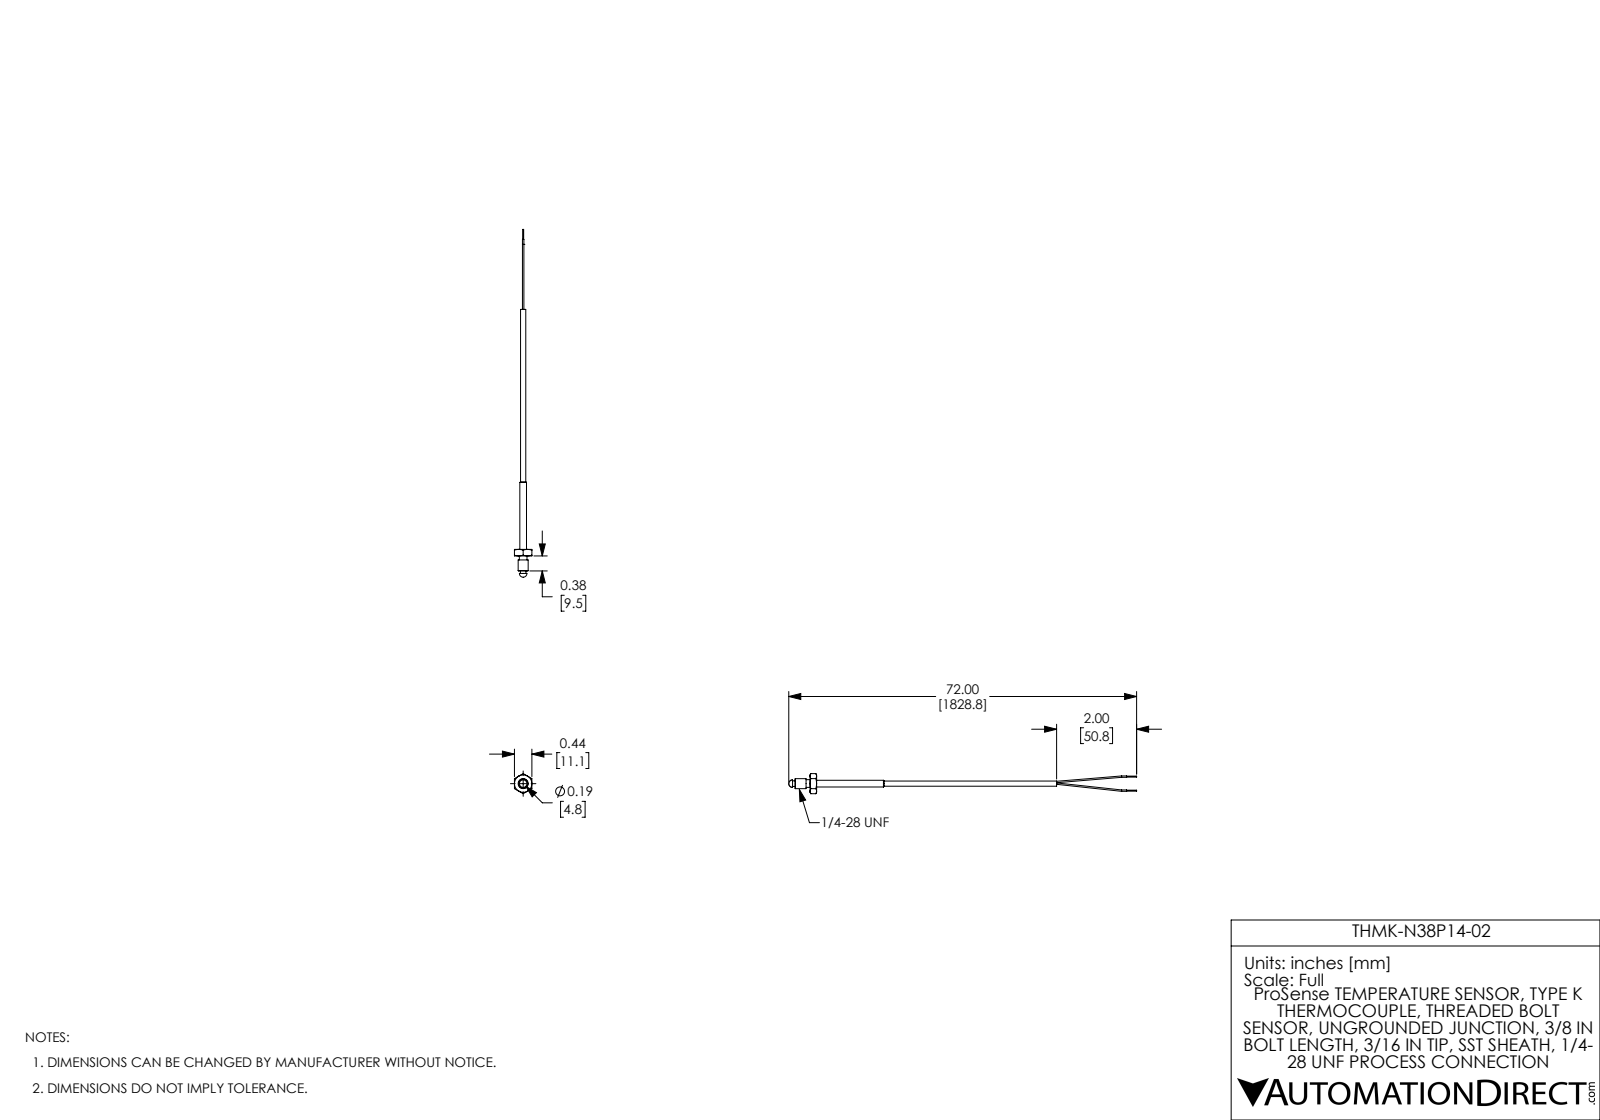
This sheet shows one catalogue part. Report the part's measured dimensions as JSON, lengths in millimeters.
{"part_name": "THMK-N38P14-02", "step_written_by": "SolidWorks 2017 (AUTOMOTIVE_DESIGN)", "units": "millimeters", "bodies": {"solids": 1, "faces": 57, "planar": 17, "cylindrical": 18, "other": 22}, "overall_size": [220.9, 12.8, 11.1], "volume_mm3": 2360, "surface_area_mm2": 2596, "round_bosses_or_shafts": [[0.6, 2], [6.4, 1], [4.9, 1], [4.3, 1], [3.6, 1], [3.3, 1], [0.9, 1], [0.9, 1]], "face_to_face_distances": [4.2, 11, 13.7, 9.5, 6.7, 2.5, 7, 15.3, 11.1, 8.6]}
